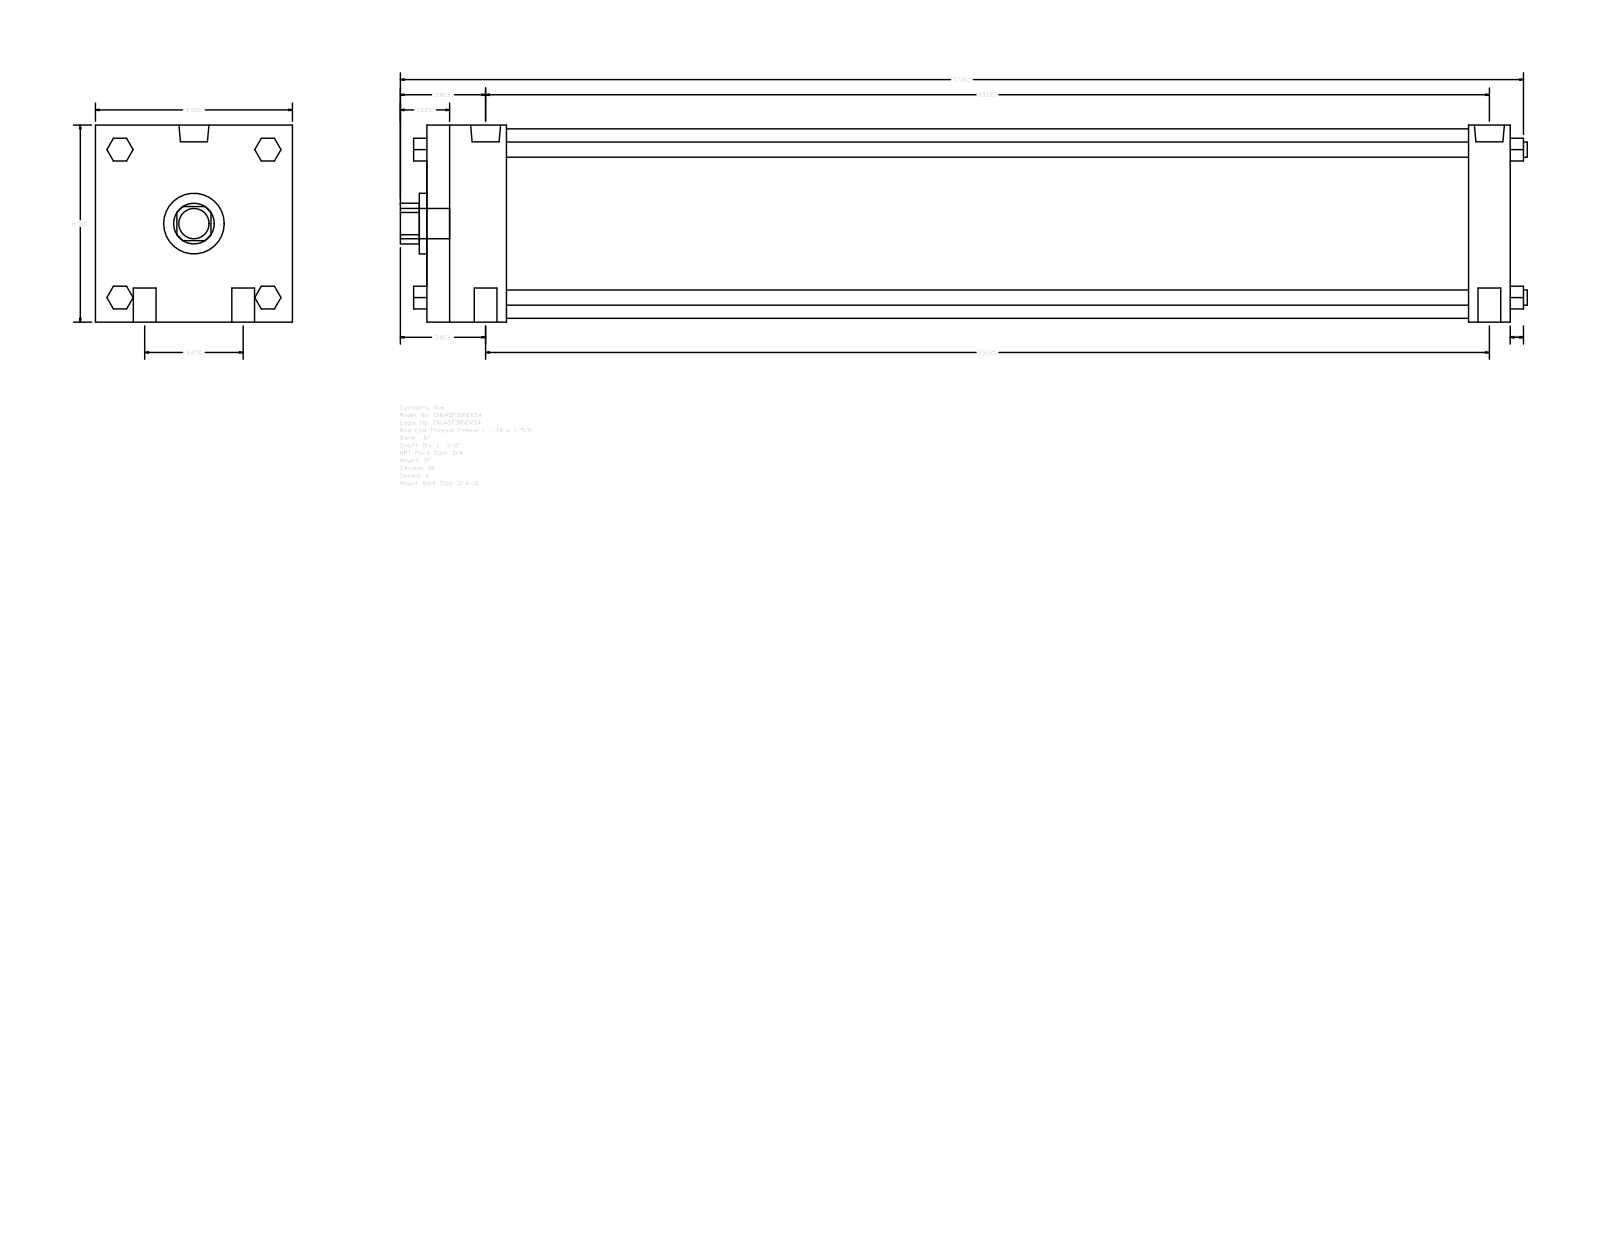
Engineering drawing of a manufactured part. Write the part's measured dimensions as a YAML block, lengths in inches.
part_name: "A_SF__0600_1.375"
step_written_by: "GSSL Pune (CONFIG_CONTROL_DESIGN)"
units: inches
bodies: {solids: 0, faces: 124, planar: 94, cylindrical: 30, other: 0}
overall_size: [37.187, 6.5, 6.5]
round_holes:
  - {diameter: 1.375, count: 1}
  - {diameter: 2, count: 1}
  - {diameter: 6.25, count: 1}
round_bosses_or_shafts:
  - {diameter: 0.75, count: 4}
  - {diameter: 0.5, count: 4}
  - {diameter: 0.989, count: 2}
  - {diameter: 0.594, count: 2}
  - {diameter: 1, count: 1}
partial_cylinders:
  - {radius: 0.672, count: 1}
face_to_face_distances: [6.5, 35.75, 34.375, 1.375, 2.625, 31.75, 33.125, 0.75, 2.44, 4.226]
